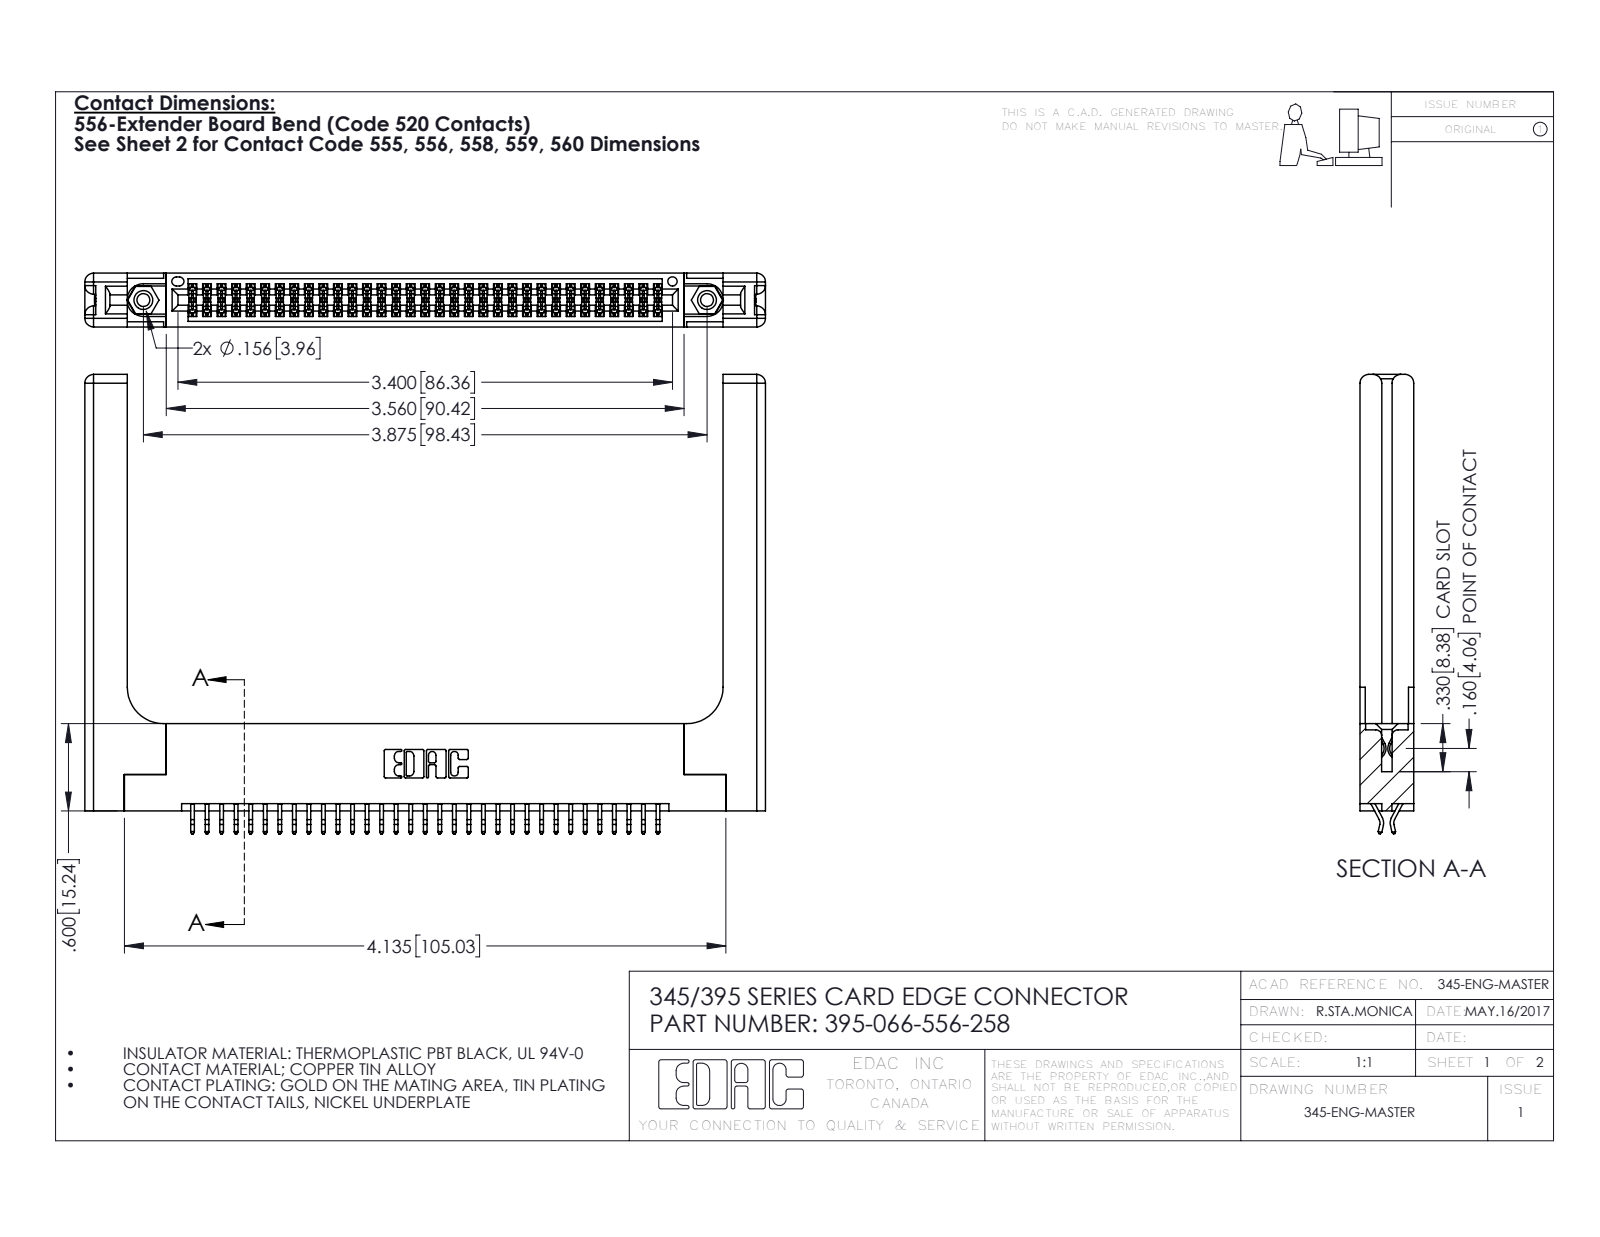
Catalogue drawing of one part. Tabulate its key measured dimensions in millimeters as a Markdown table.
| quantity | value |
| --- | --- |
| part name | 395-066-556-258; 345-220-058_345-220-058; 345-292-001_556 Tail; 345-250-001_345-250-001-102 (+1 more) |
| STEP written by | SolidWorks 2016 (CONFIG_CONTROL_DESIGN) |
| units | millimeters |
| bodies | 71 solids, 4078 faces (2670 planar, 1348 cylindrical, 60 other) |
| overall size | 118.8 × 80.2 × 9.4 |
| volume | 19 930 mm³ |
| surface area | 21 770 mm² |
| round holes (diameter × count) | 2.3 × 2, 3.2 × 2, 4 × 2, 1.6 × 1 |
| round bosses / shafts (diameter × count) | 3.9 × 2 |
| partial cylindrical surfaces (radius × count) | 0.2 × 99, 0.3 × 22, 1.5 × 16, 0.2 × 6, 0.8 × 6, 0.7 × 3, 0.3 × 2, 0.4 × 2 |
| main face-to-face distances | 9.4, 1.8, 7.6, 5.1, 0.6, 5.7, 2.5, 6.9, 3.8, 3.8 |
| hole center spacings | 6.9, 92.5, 98.4 |
